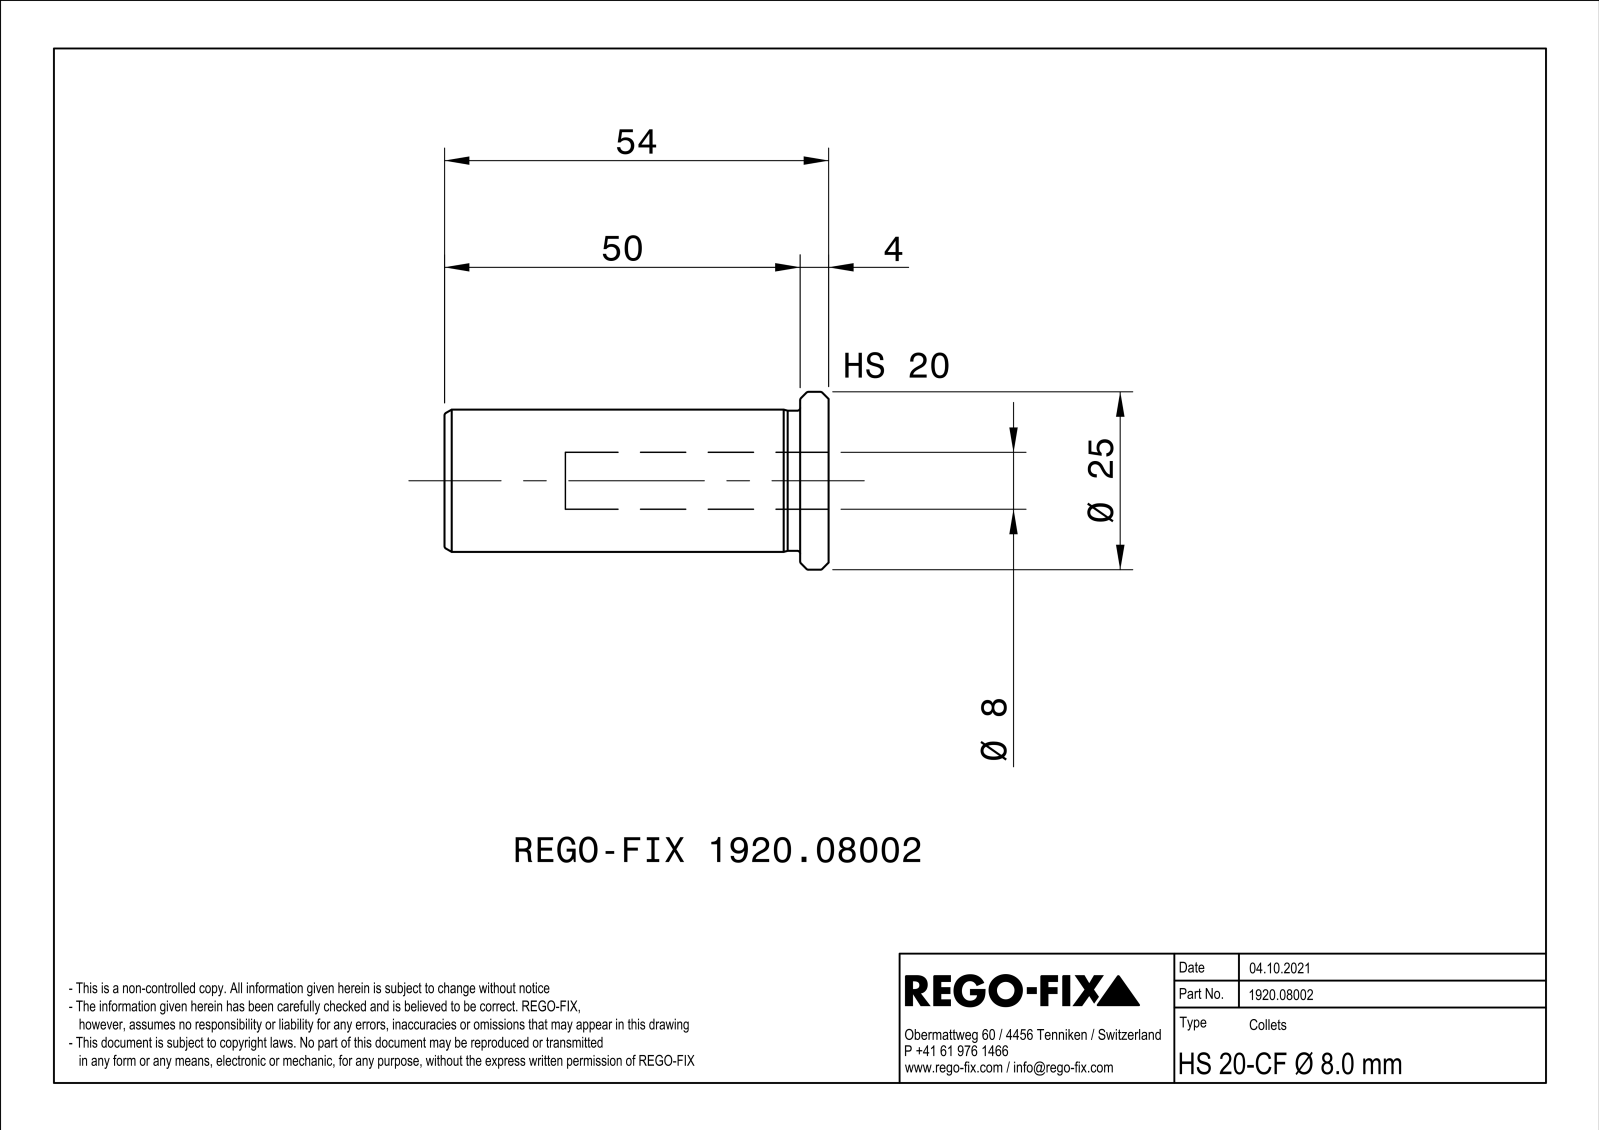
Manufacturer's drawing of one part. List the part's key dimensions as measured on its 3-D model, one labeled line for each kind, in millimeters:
Part name (STEP PRODUCT): NOCUT
STEP written by: SIEMENS PLM Software Solid Edge ST10 (AUTOMOTIVE_DESIGN)
Units: millimetres
Bodies: 1 solid, 82 faces (22 planar, 19 cylindrical, 41 other)
Overall size (bounding box): 54 × 24.98 × 24.98
Volume: 12 026 mm³ · Surface area: 7 134 mm²
Round holes (diameter × count): ⌀8 ×1, ⌀10.5 ×1, ⌀16.5 ×1
Round bosses / shafts (diameter × count): ⌀25 ×1, ⌀20 ×1, ⌀19.7 ×1
Partial cylindrical surfaces — rounded edges, fillets, slot ends (radius × count): R0.5 ×4
Main face-to-face distances: 1, 4, 54, 50
